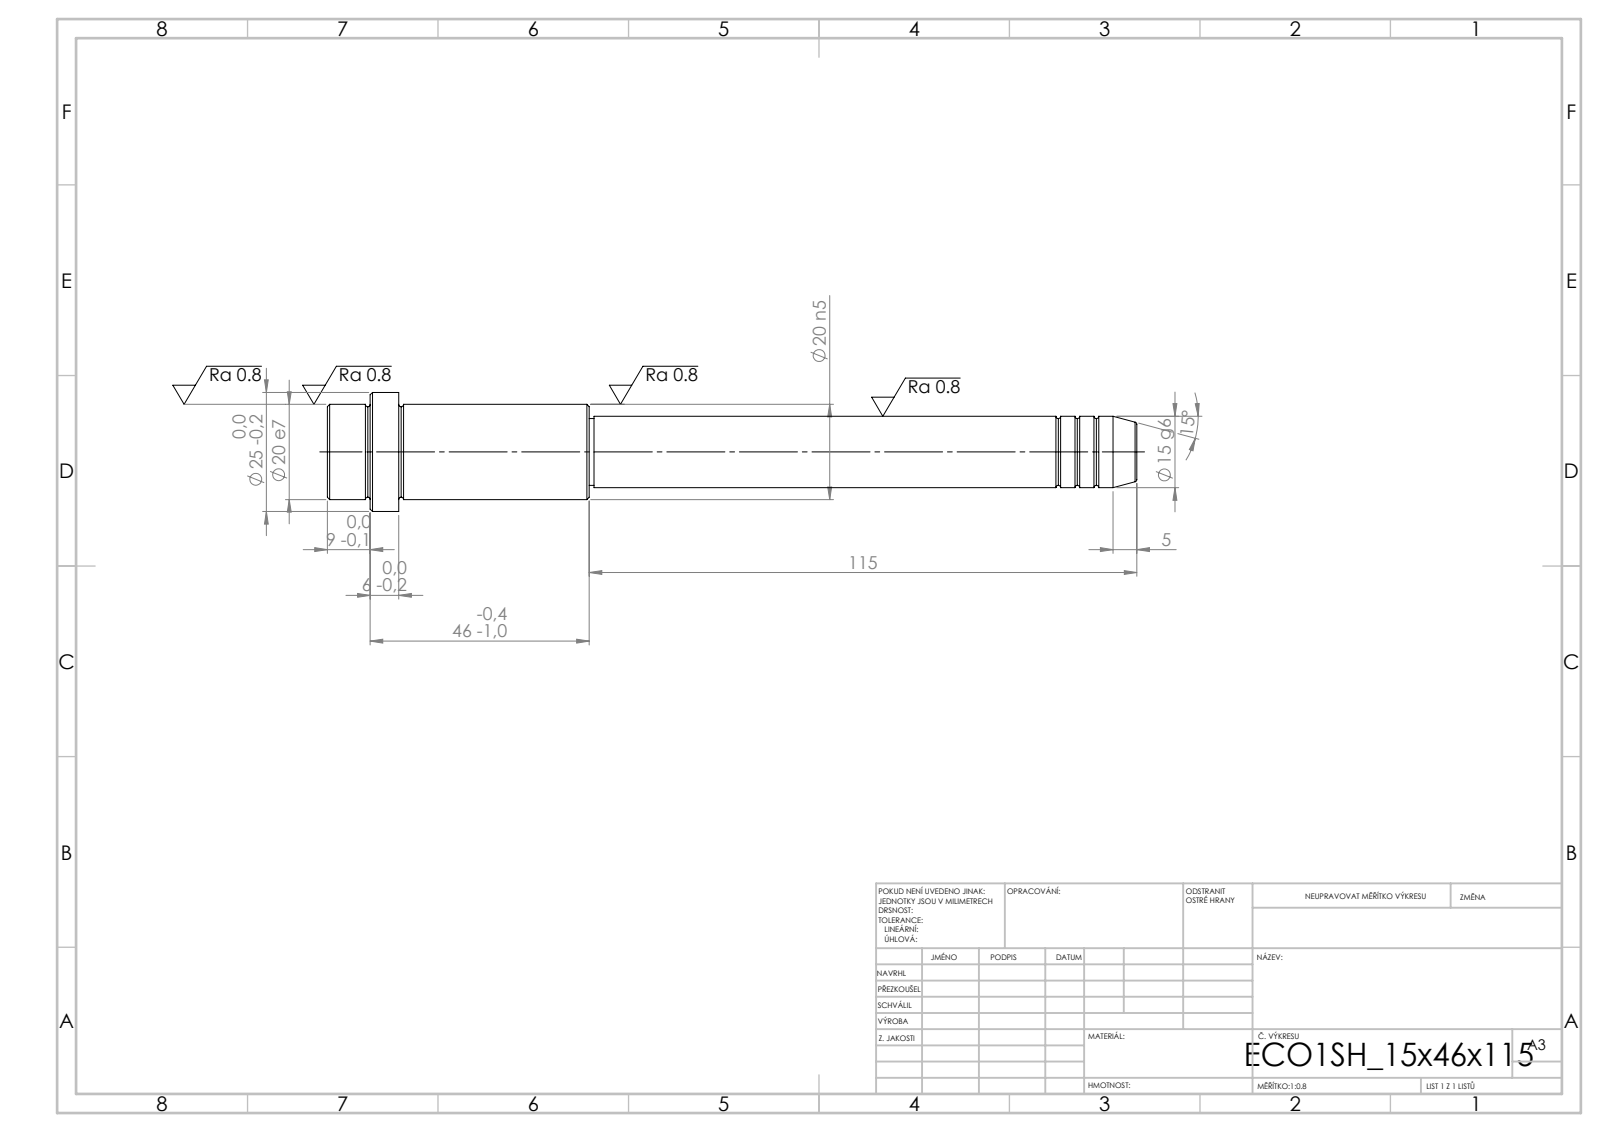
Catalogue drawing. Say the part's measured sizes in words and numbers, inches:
Its 3-D file was written by "SolidWorks 2019 (CONFIG_CONTROL_DESIGN)". It is 1 solid with 52 faces: 6 planar, 16 cylindrical and 30 other. Overall it measures 6.693 by 0.984 by 0.984 inches. Its volume is 2.341 cubic inches and its surface area 15.49 square inches. Round bosses or shafts: 1 of diameter 0.984, 1 of diameter 0.787, 1 of diameter 0.591, 1 of diameter 0.551. The main face-to-face distances are 0.591, 0.236, 0.354, 1.575, 1.811, 2.165, 4.528, 6.102, 6.339, 6.693.
